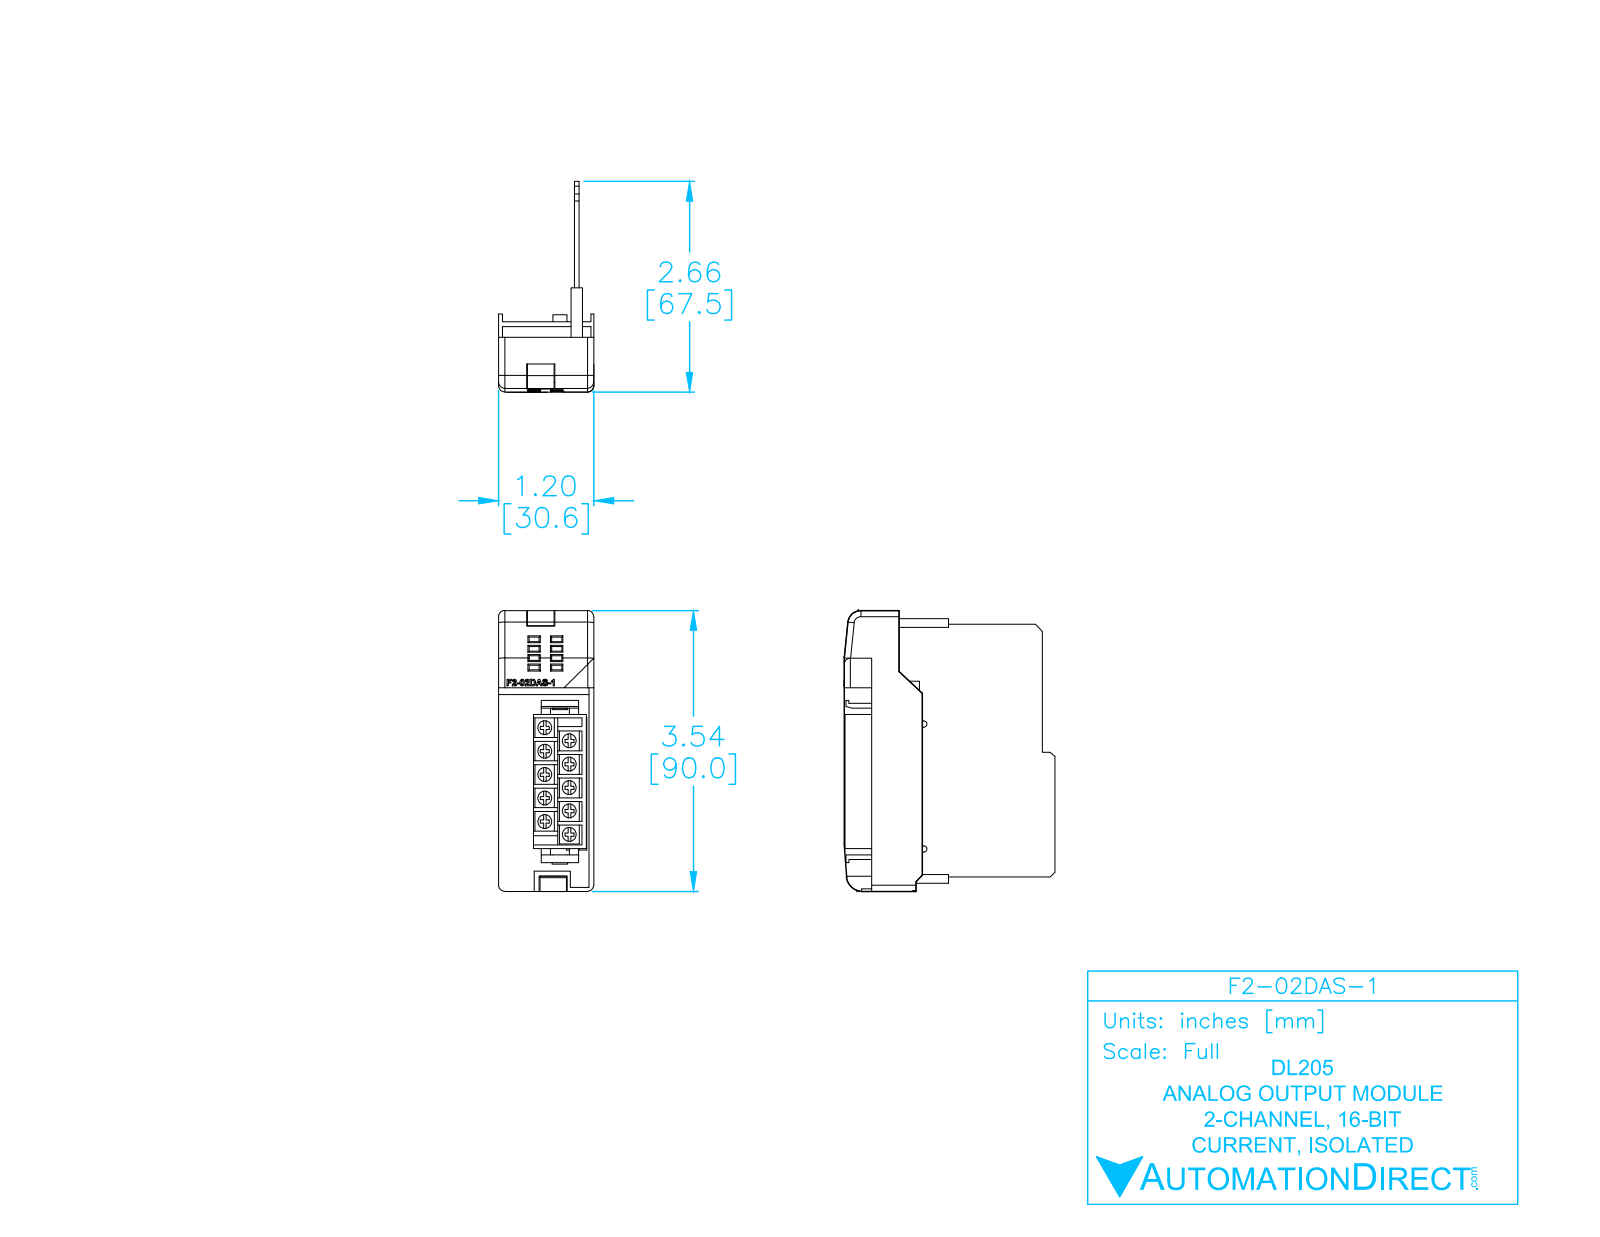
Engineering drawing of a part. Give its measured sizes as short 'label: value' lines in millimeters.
name: F2-02DAS-1_ModuleCase_light_NEW
written by: SolidWorks 2009 (AUTOMOTIVE_DESIGN)
unit: mm
bodies: 6 solids, 592 faces (417 planar, 75 cylindrical, 100 other)
size: 90 × 67.61 × 30.55
volume: 25 374 mm³; area: 28 533 mm²
bosses: 10× ⌀4.5
rounds: 16× R0.35, 9× R2, 2× R0.25, 2× R1, 2× R1.25, 1× R4.12, 1× R5.39
face distances: 1.5, 4.72, 6.22, 2.37, 3.87, 2.35, 3.22, 0.85, 8.14, 24.28
